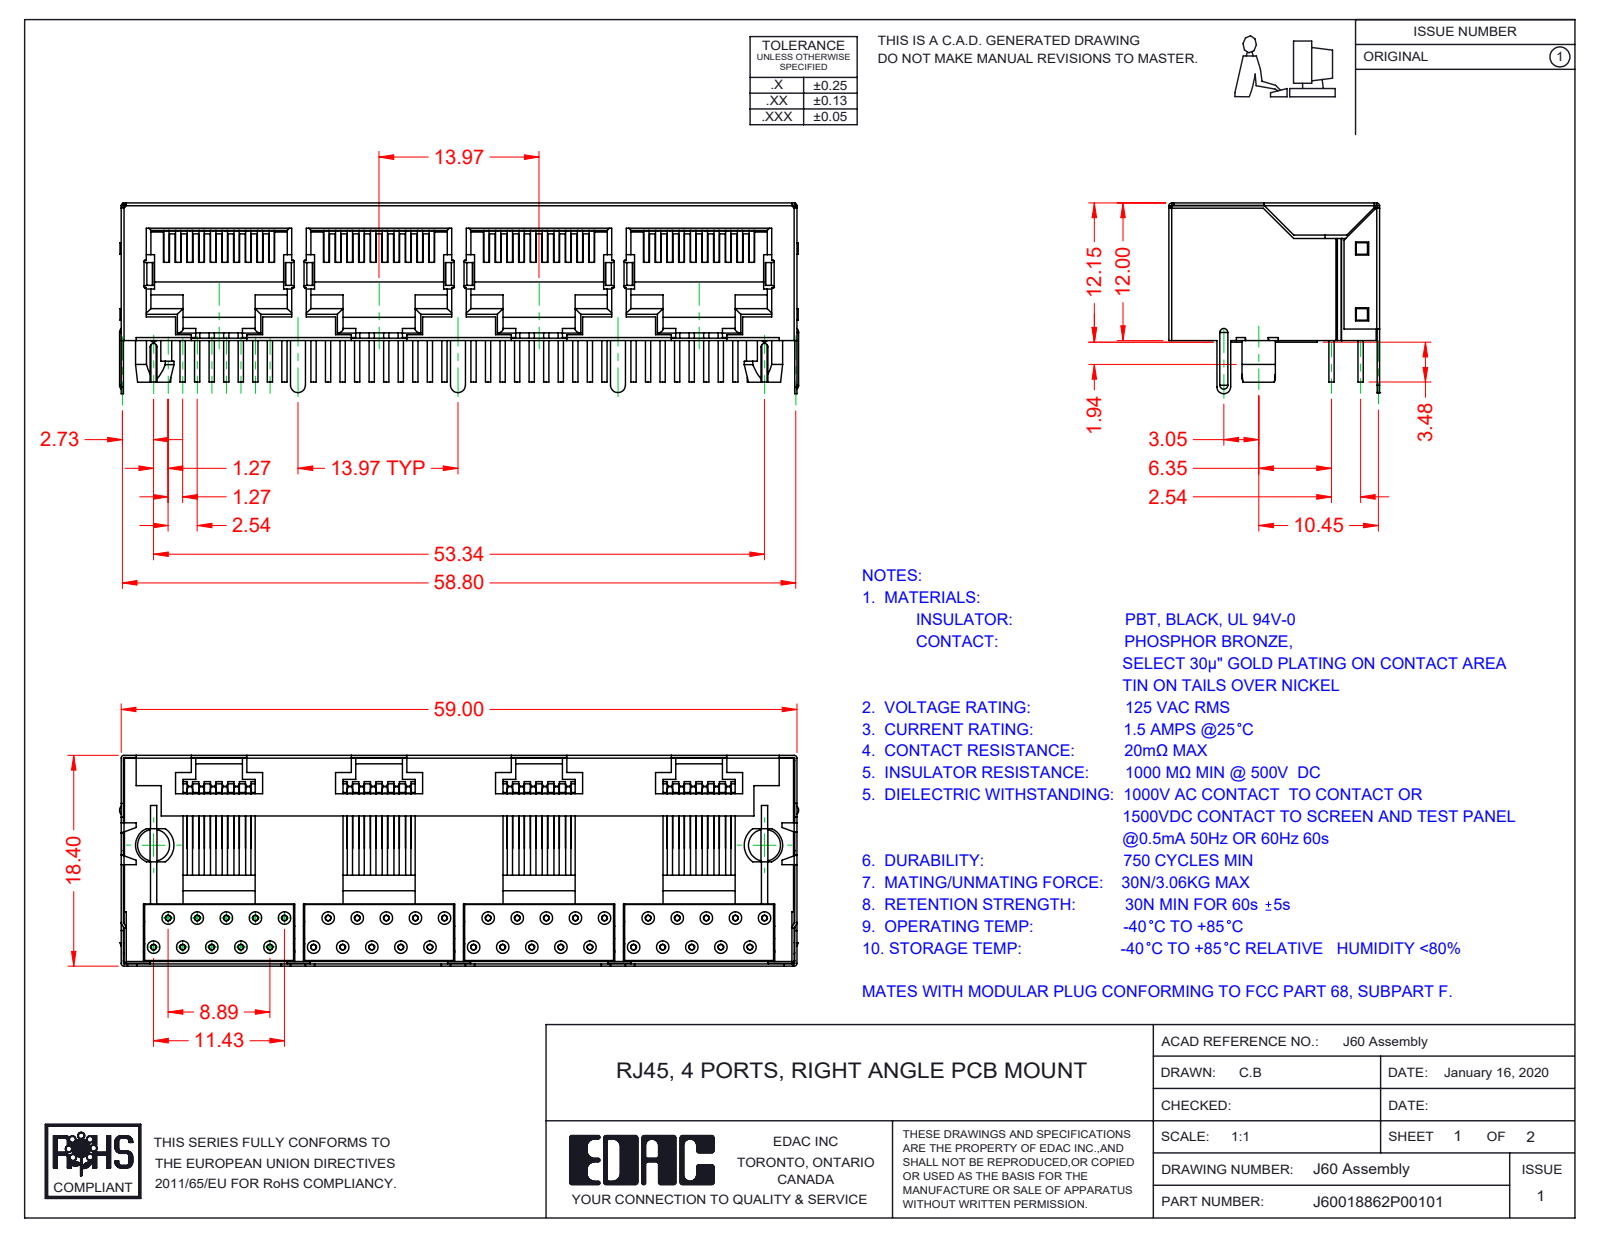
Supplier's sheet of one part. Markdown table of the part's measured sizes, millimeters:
| quantity | value |
| --- | --- |
| part name | 60 Shield; 60 Insulator; RJ60041162P00101; 60 Contacts_10P10C |
| STEP written by | SolidWorks 2016 (CONFIG_CONTROL_DESIGN) |
| units | millimeters |
| bodies | 42 solids, 2674 faces (1505 planar, 763 cylindrical, 406 other) |
| overall size | 59.3 × 18.4 × 16.65 |
| volume | 7 062 mm³ |
| surface area | 18 987 mm² |
| round holes (diameter × count) | 0.5 × 40, 1.1 × 40 |
| round bosses / shafts (diameter × count) | 0.46 × 120 |
| partial cylindrical surfaces (radius × count) | 0.3 × 26, 0.25 × 21, 0.5 × 18, 0.1 × 16, 0.21 × 10, 0.8 × 7, 0.65 × 3, 0.28 × 2 |
| main face-to-face distances | 0.5, 11.75, 11.55, 13.97, 2.19, 5.38, 5.18, 4.88, 18.2, 11.5 |
| hole center spacings | 2.84, 2.54, 4.58, 13.97, 5.08, 12.95, 15.45, 11.43 |
